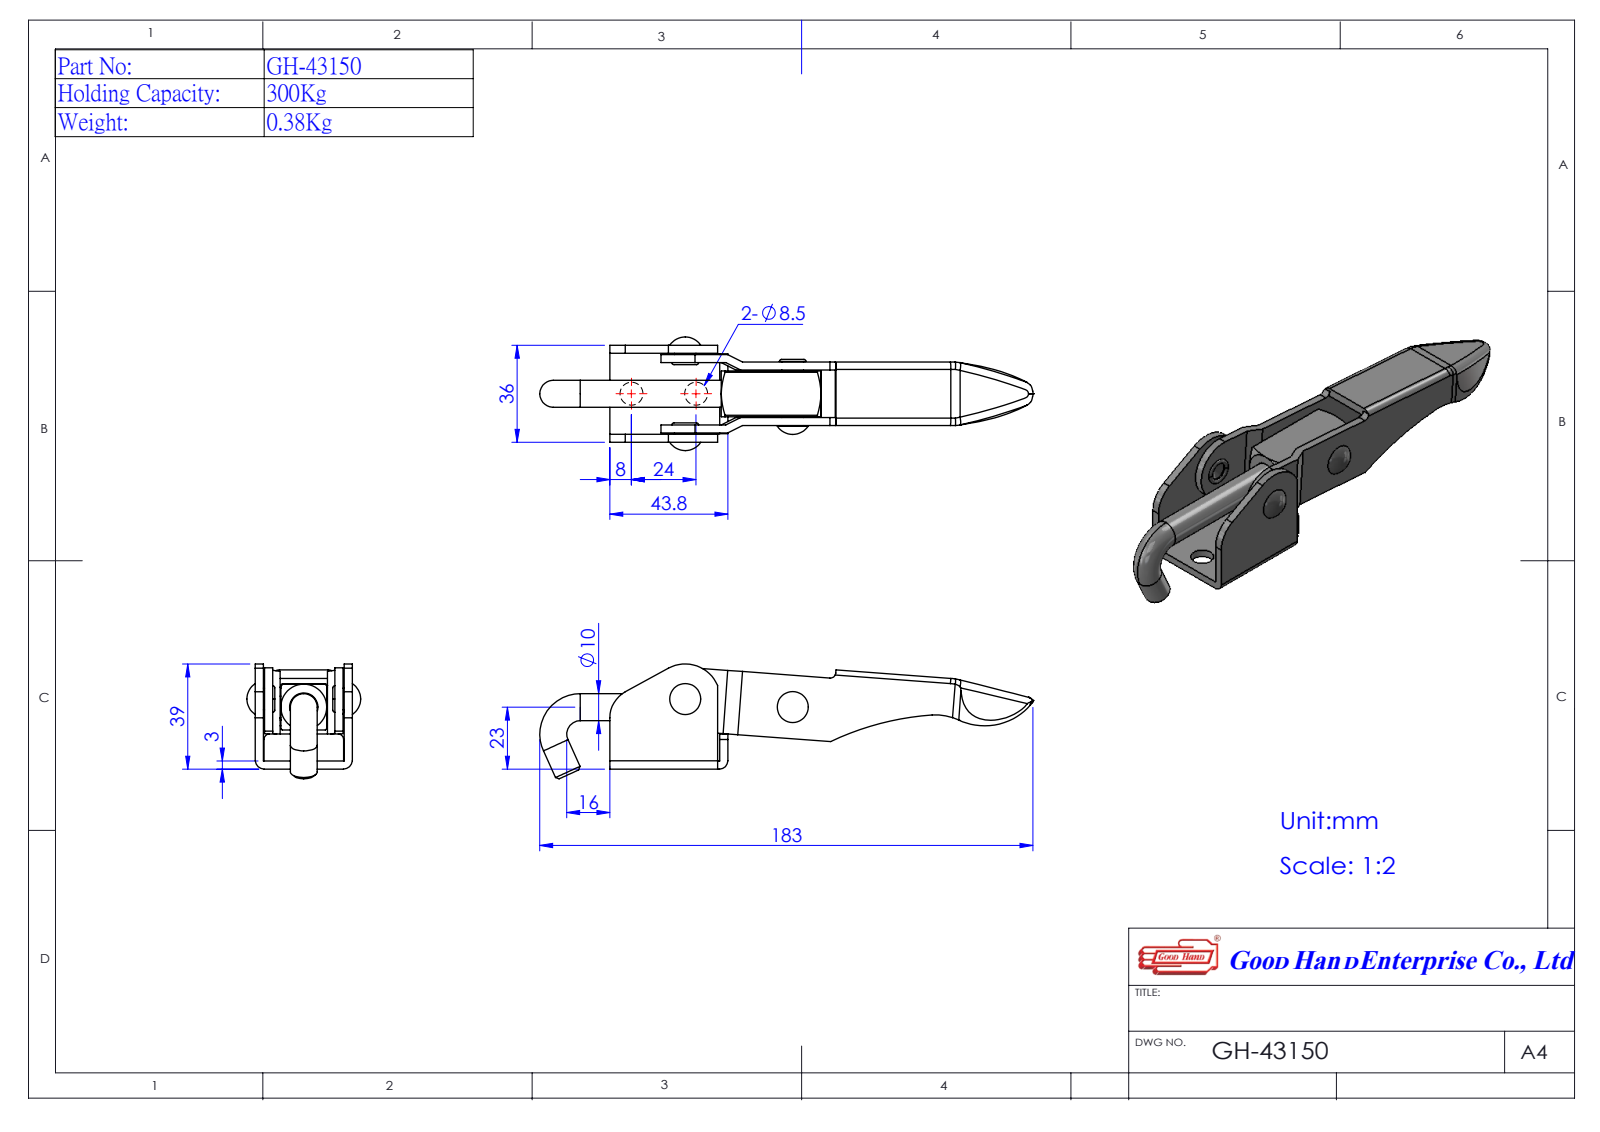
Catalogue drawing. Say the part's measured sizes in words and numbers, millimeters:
The part is named "GH-43150(簡化); 44315044; Group3^GH-43150(簡化); Group2^GH-43150(簡化) (+1 more)". Its 3-D file was written by "SolidWorks 2016 (AUTOMOTIVE_DESIGN)". It is 9 solids with 212 faces: 77 planar, 66 cylindrical and 69 other. Overall it measures 183.13 by 42.62 by 42.2 millimeters. Its volume is 49 979 cubic millimeters and its surface area 32 527 square millimeters. Round holes: 4 of diameter 8.5, 2 of diameter 6, 1 of diameter 10. Round bosses or shafts: 1 of diameter 10, 1 of diameter 8. Partial cylindrical surfaces (rounded edges, fillets, slot ends): 3 of radius 2, 2 of radius 3, 2 of radius 3.31, 2 of radius 3.5, 2 of radius 20, 1 of radius 3.1, 1 of radius 11, 1 of radius 11.75. The main face-to-face distances are 3, 26.8, 6.2, 20.6, 3.2, 23.8, 29.8, 9.2, 33, 3.45. The hole center spacings are 24, 40.
